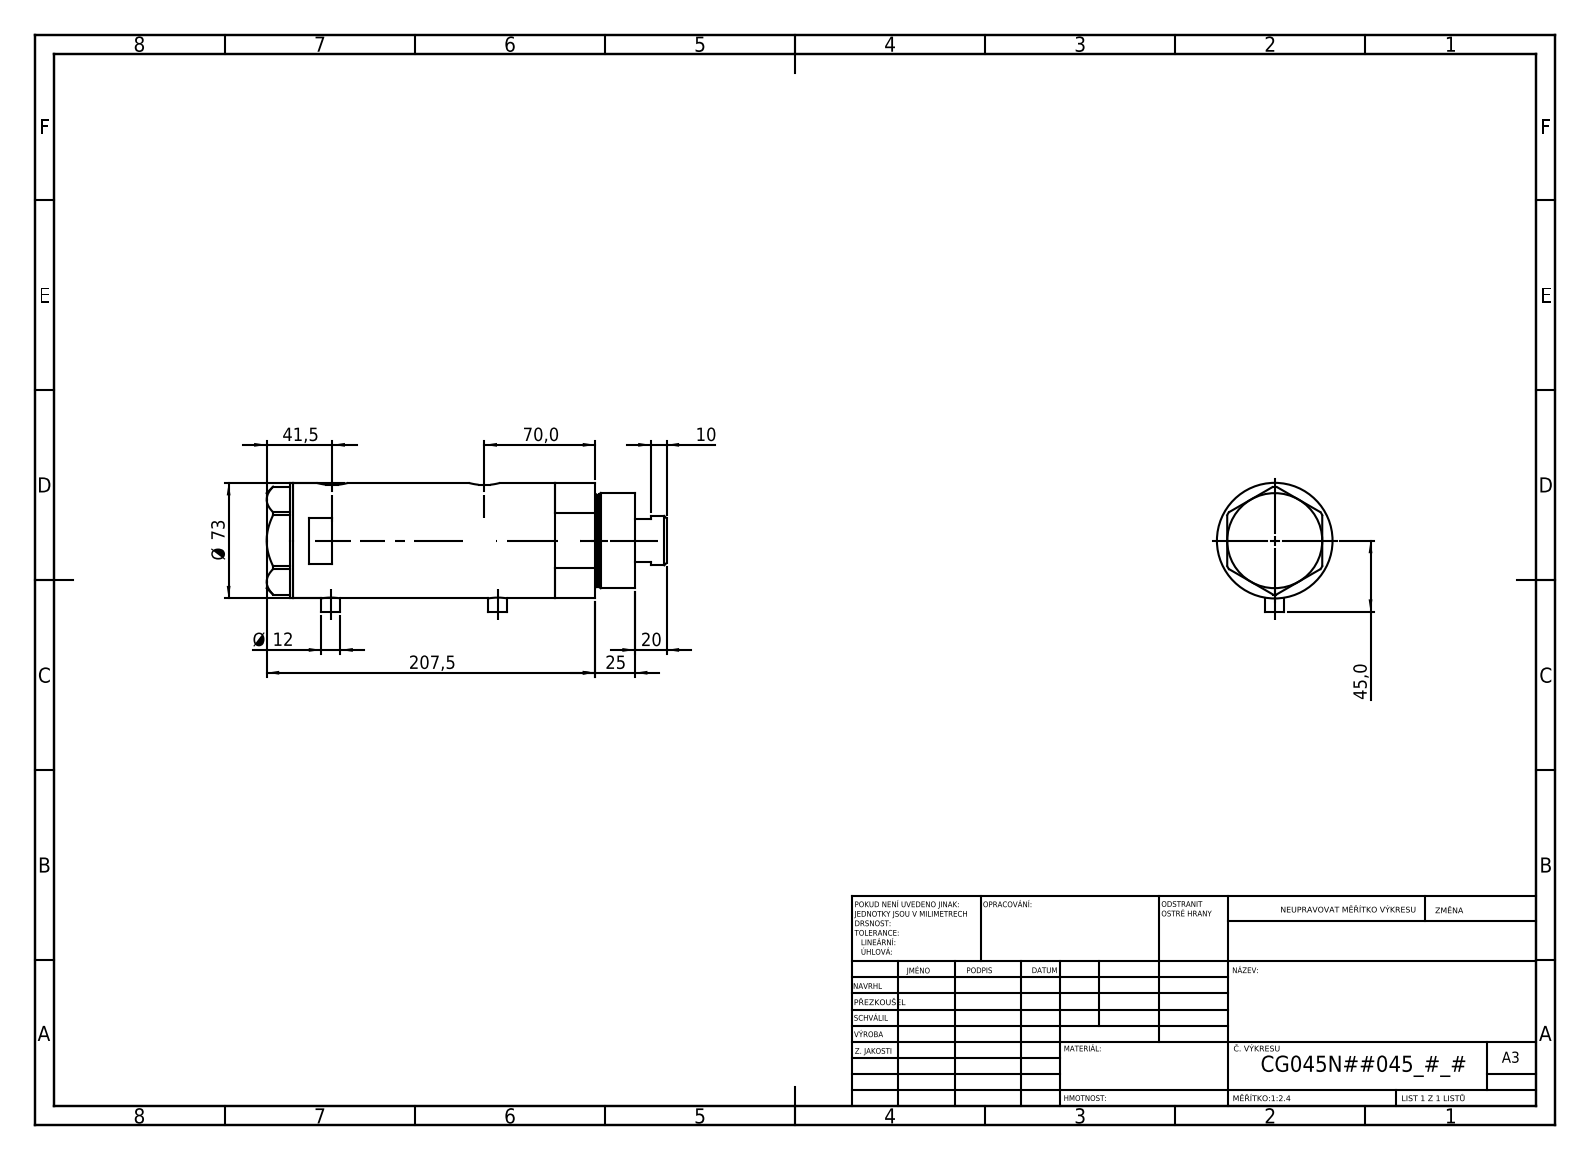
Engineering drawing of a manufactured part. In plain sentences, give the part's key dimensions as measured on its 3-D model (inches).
The part is named "V270CG_FRONT; V270CG_BACK; V270CG_MIDDLE; V270CG_VC". Its 3-D file was written by "SolidWorks 2019 (CONFIG_CONTROL_DESIGN)". It is 4 solids with 120 faces: 49 planar, 51 cylindrical and 20 other. Overall it measures 9.941 by 3.209 by 2.874 inches. Its volume is 54.32 cubic inches and its surface area 231.2 square inches. Round holes: 2 of diameter 0.492, 2 of diameter 0.518, 1 of diameter 0.413, 1 of diameter 1.26, 1 of diameter 1.319, 1 of diameter 1.772, 1 of diameter 1.89, 1 of diameter 2.52. Round bosses or shafts: 2 of diameter 0.472, 1 of diameter 2.874, 1 of diameter 2.362, 1 of diameter 2.283, 1 of diameter 1.22. Partial cylindrical surfaces (rounded edges, fillets, slot ends): 2 of radius 0.394. The main face-to-face distances are 3.74, 4.764, 1.024, 0.65, 1.673, 5.413, 0.079, 8.504, 9.154, 7.48. The hole center spacings are 0.039, 0.335, 3.78, 3.819, 4.114, 4.154.
